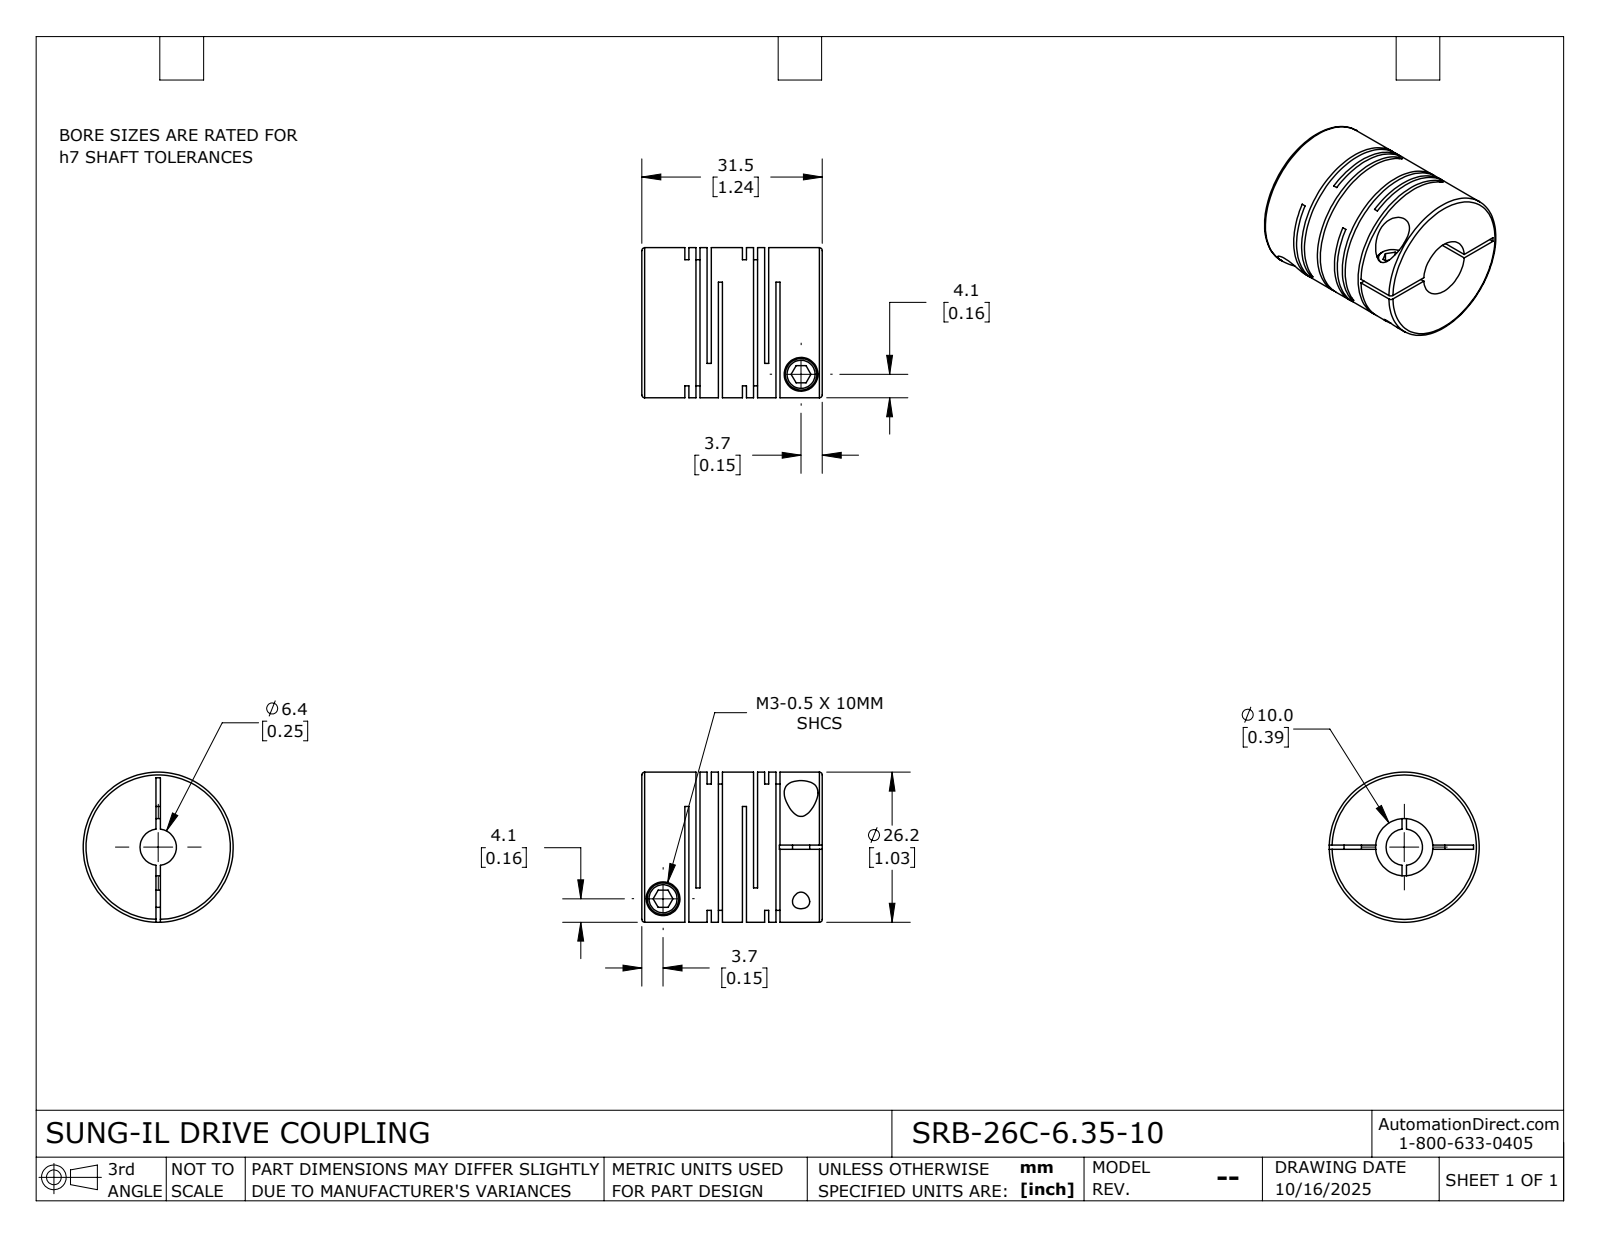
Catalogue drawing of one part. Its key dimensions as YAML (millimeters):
part_name: "SRB-26C-6.35-10"
step_written_by: "SolidWorks 2024 (CONFIG_CONTROL_DESIGN)"
units: millimeters
bodies: {solids: 1, faces: 115, planar: 60, cylindrical: 42, other: 13}
overall_size: [31.5, 26.2, 26.2]
volume: 12273
surface_area: 10781
round_holes:
  - {diameter: 3, count: 2}
  - {diameter: 5.9, count: 2}
  - {diameter: 6.35, count: 1}
  - {diameter: 10, count: 1}
round_bosses_or_shafts:
  - {diameter: 5.5, count: 2}
  - {diameter: 26.2, count: 1}
face_to_face_distances: [1.95, 10.05, 0.71, 3.9, 8.1, 12, 1.24, 2.66, 9.34, 13.95]
